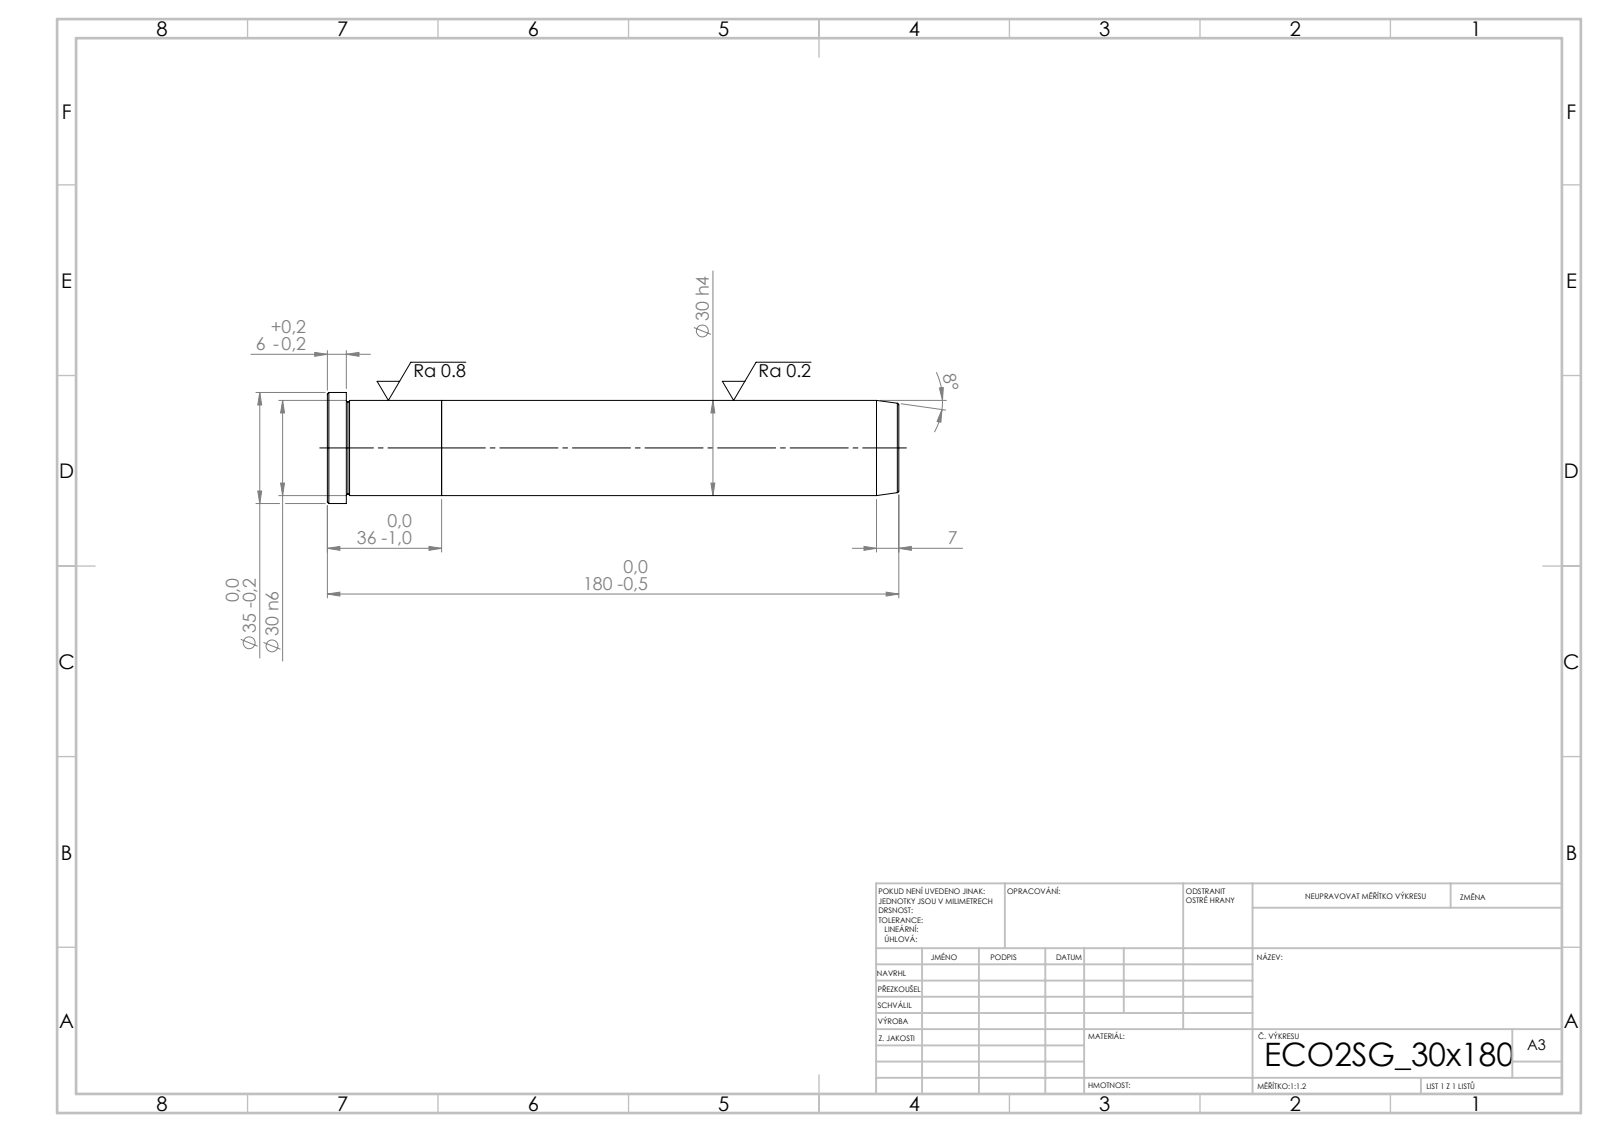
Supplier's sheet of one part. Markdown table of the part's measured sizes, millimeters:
| quantity | value |
| --- | --- |
| STEP written by | SolidWorks 2019 (CONFIG_CONTROL_DESIGN) |
| units | millimeters |
| bodies | 2 solids, 21 faces (5 planar, 6 cylindrical, 10 other) |
| overall size | 180 × 35 × 35 |
| volume | 128 395 mm³ |
| surface area | 20 296 mm² |
| round bosses / shafts (diameter × count) | 35 × 1, 30 × 1 |
| main face-to-face distances | 36, 144, 180, 174, 30, 6 |
